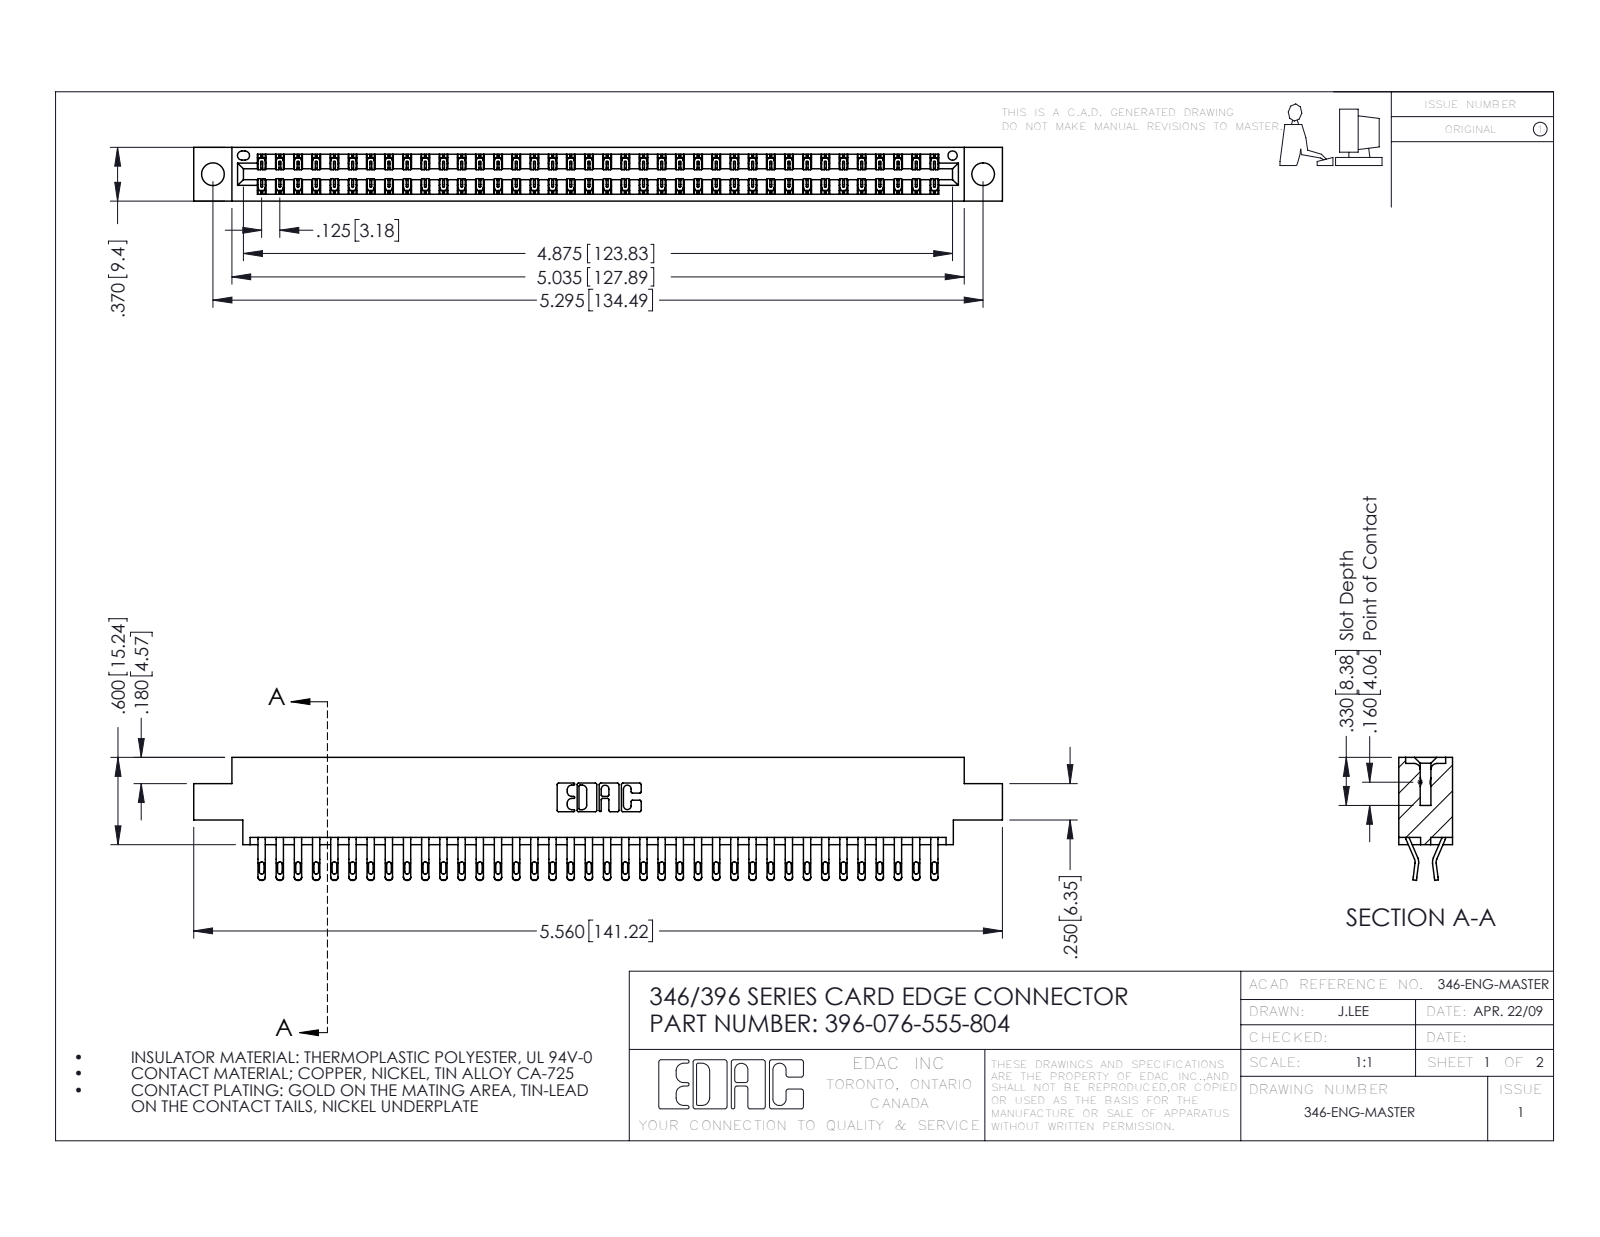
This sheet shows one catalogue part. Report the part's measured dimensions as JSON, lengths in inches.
{"part_name": "396-076-555-804; 346 Part_0.170 Offset - 0.156 Dia-TH; 345-292-001_555 Tail", "step_written_by": "SolidWorks 2016 (CONFIG_CONTROL_DESIGN)", "units": "inches", "bodies": {"solids": 77, "faces": 4534, "planar": 2588, "cylindrical": 1946, "other": 0}, "overall_size": [5.56, 0.845, 0.37], "volume_in3": 0.837, "surface_area_in2": 30.34, "round_holes": [[0.156, 2], [0.064, 1]], "partial_cylinders_radius": [[0.016, 152], [0.02, 152], [0.006, 114], [0.01, 22], [0.007, 6], [0.031, 6], [0.026, 3], [0.01, 2]], "face_to_face_distances": [0.048, 0.322, 0.37, 0.25, 0.025, 0.072, 0.298, 0.275, 0.148, 0.222], "hole_center_spacings": [0.246, 5.086, 5.295]}
